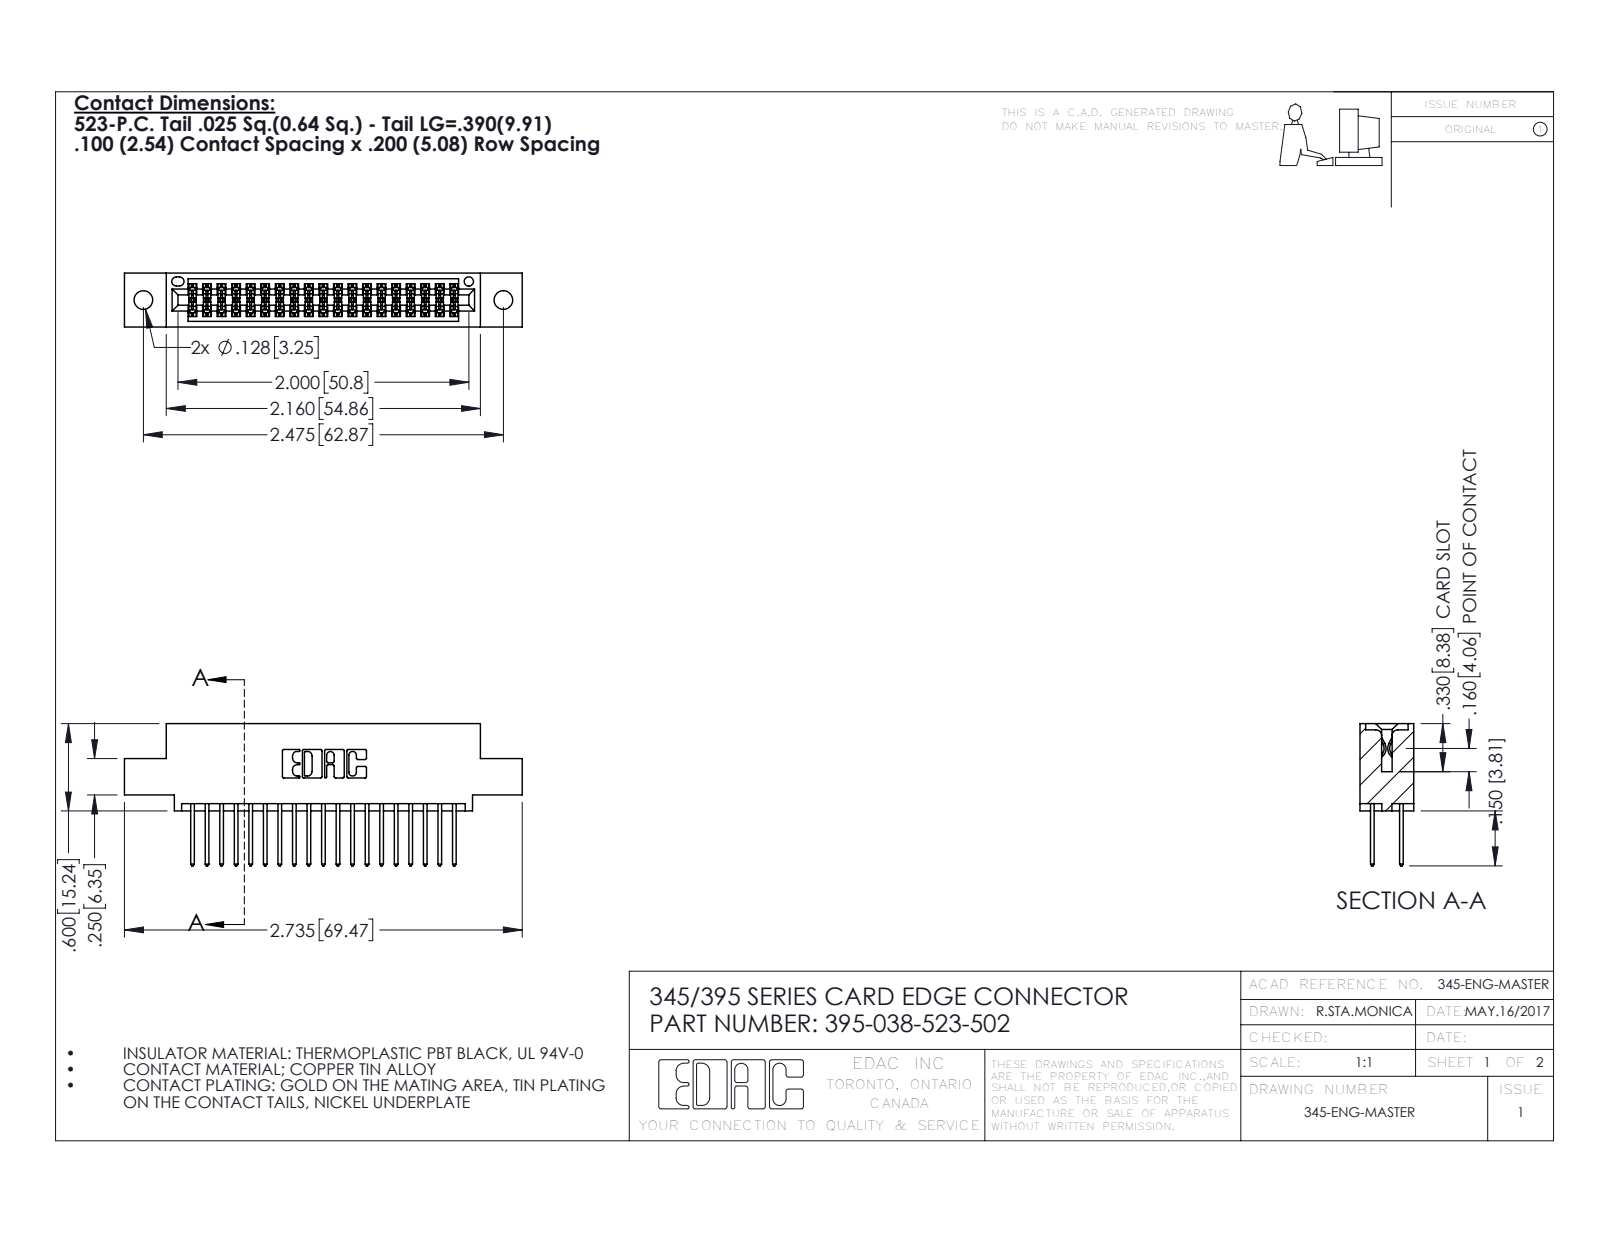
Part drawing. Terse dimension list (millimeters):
name: 345 Part_0.110 Offset - 0.128 Dia; 395-038-523-502; 345-292-001_345-293-123
written by: SolidWorks 2016 (CONFIG_CONTROL_DESIGN)
unit: mm
bodies: 39 solids, 2030 faces (1338 planar, 692 cylindrical, 0 other)
size: 69.5 × 24.8 × 9.4
volume: 6 510 mm³; area: 9 335 mm²
holes: 2× ⌀3.3, 1× ⌀1.6
rounds: 57× R0.2, 38× R0.3, 22× R0.3, 6× R0.2, 6× R0.8, 3× R0.7, 2× R0.4, 2× R0.5
face distances: 7.6, 1.8, 5.1, 2.5, 6.9, 0.6, 9.4, 5.7, 4.4, 3.8
hole spacings: 6.9, 56.9, 62.9
